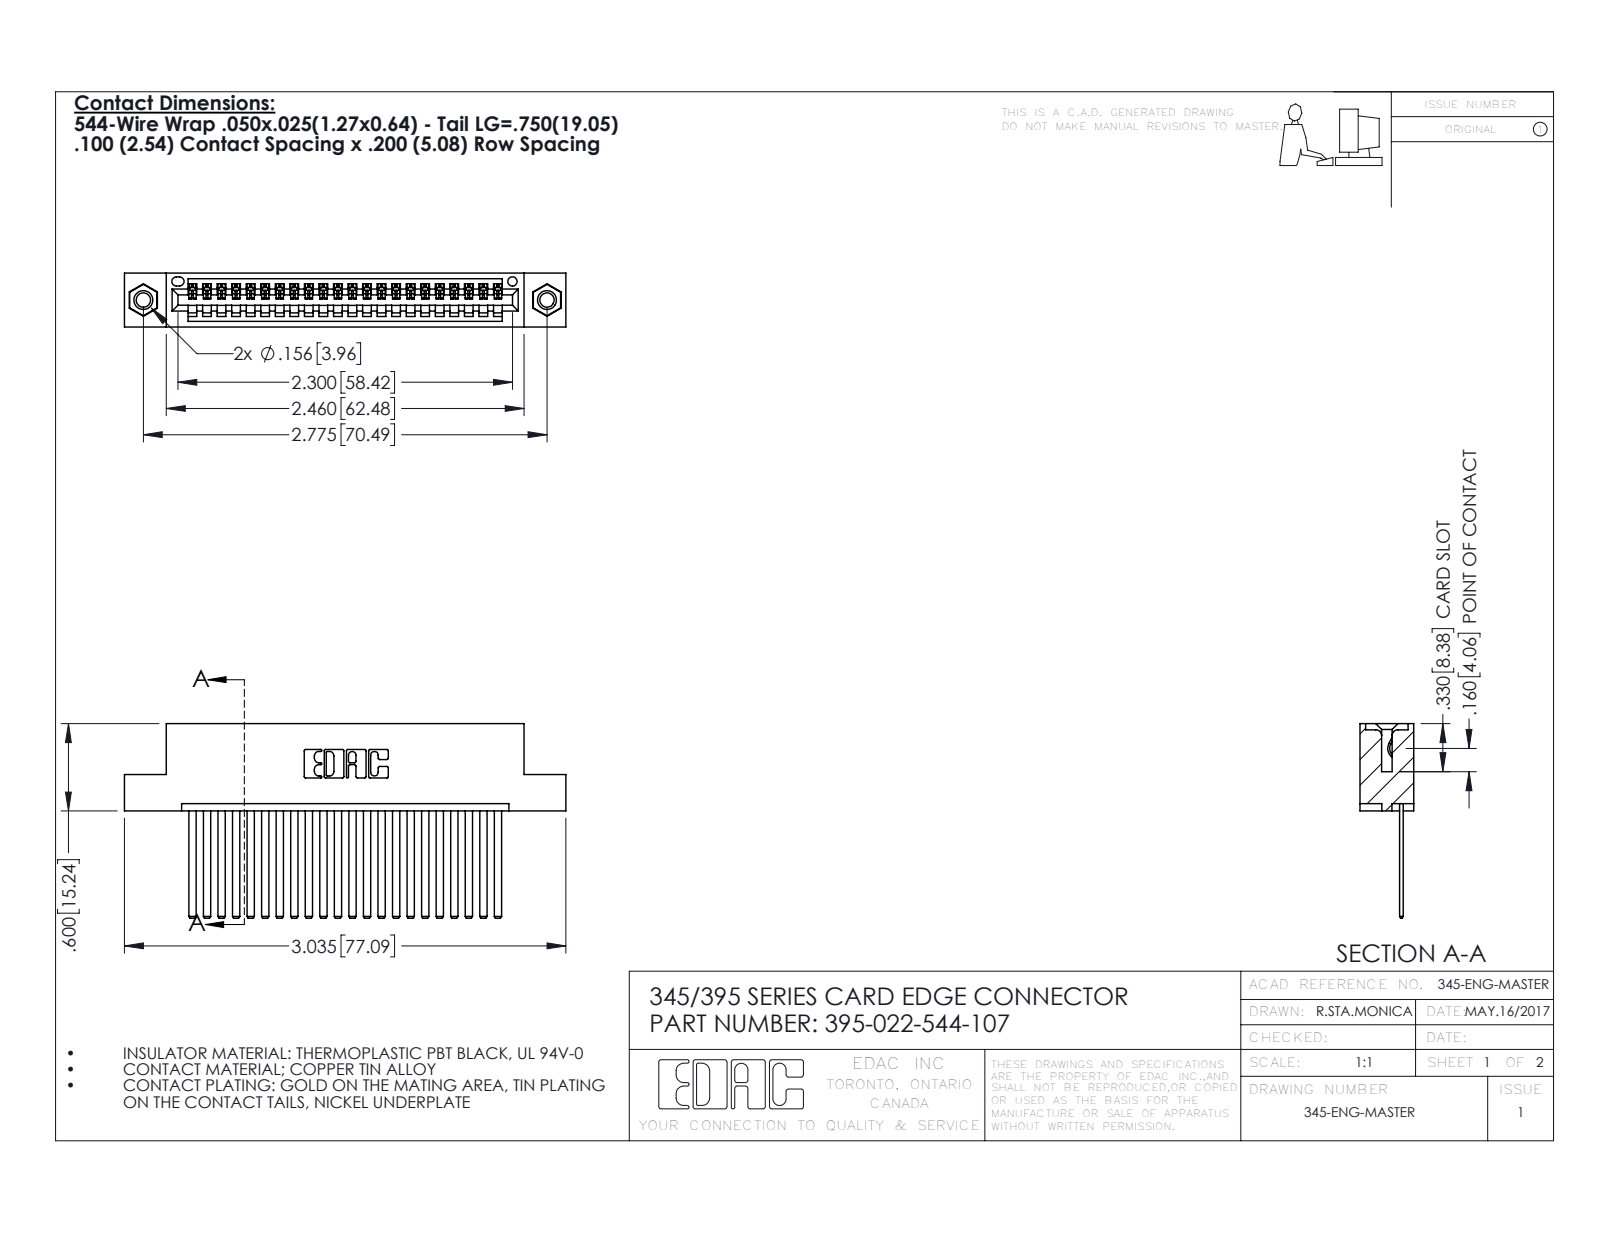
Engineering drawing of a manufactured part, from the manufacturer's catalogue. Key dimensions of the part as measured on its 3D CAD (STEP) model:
Part name (STEP PRODUCT): 345-292-001_345-293-144; 395-022-544-107; 345 Part_Flush Mounting Lugs - 0.156 Dia-TI; 345-250-001_345-250-005-103
STEP written by: SolidWorks 2016 (CONFIG_CONTROL_DESIGN)
Units: inches
Bodies: 25 solids, 1330 faces (904 planar, 410 cylindrical, 16 other)
Overall size (bounding box): 3.035 × 1.337 × 0.37
Volume: 0.452 in³ · Surface area: 16.06 in²
Round holes (diameter × count): ⌀0.098 ×2, ⌀0.125 ×2, ⌀0.156 ×2, ⌀0.064 ×1
Round bosses / shafts (diameter × count): ⌀0.155 ×2
Partial cylindrical surfaces — rounded edges, fillets, slot ends (radius × count): R0.006 ×44, R0.01 ×22, R0.007 ×6, R0.031 ×6, R0.026 ×3, R0.031 ×2, R0.04 ×2, R0.014 ×1
Main face-to-face distances: 0.072, 0.298, 0.098, 0.272, 0.025, 0.2, 0.37, 0.225, 0.149, 0.072
Hole centre spacings: 0.27, 2.541, 2.775
